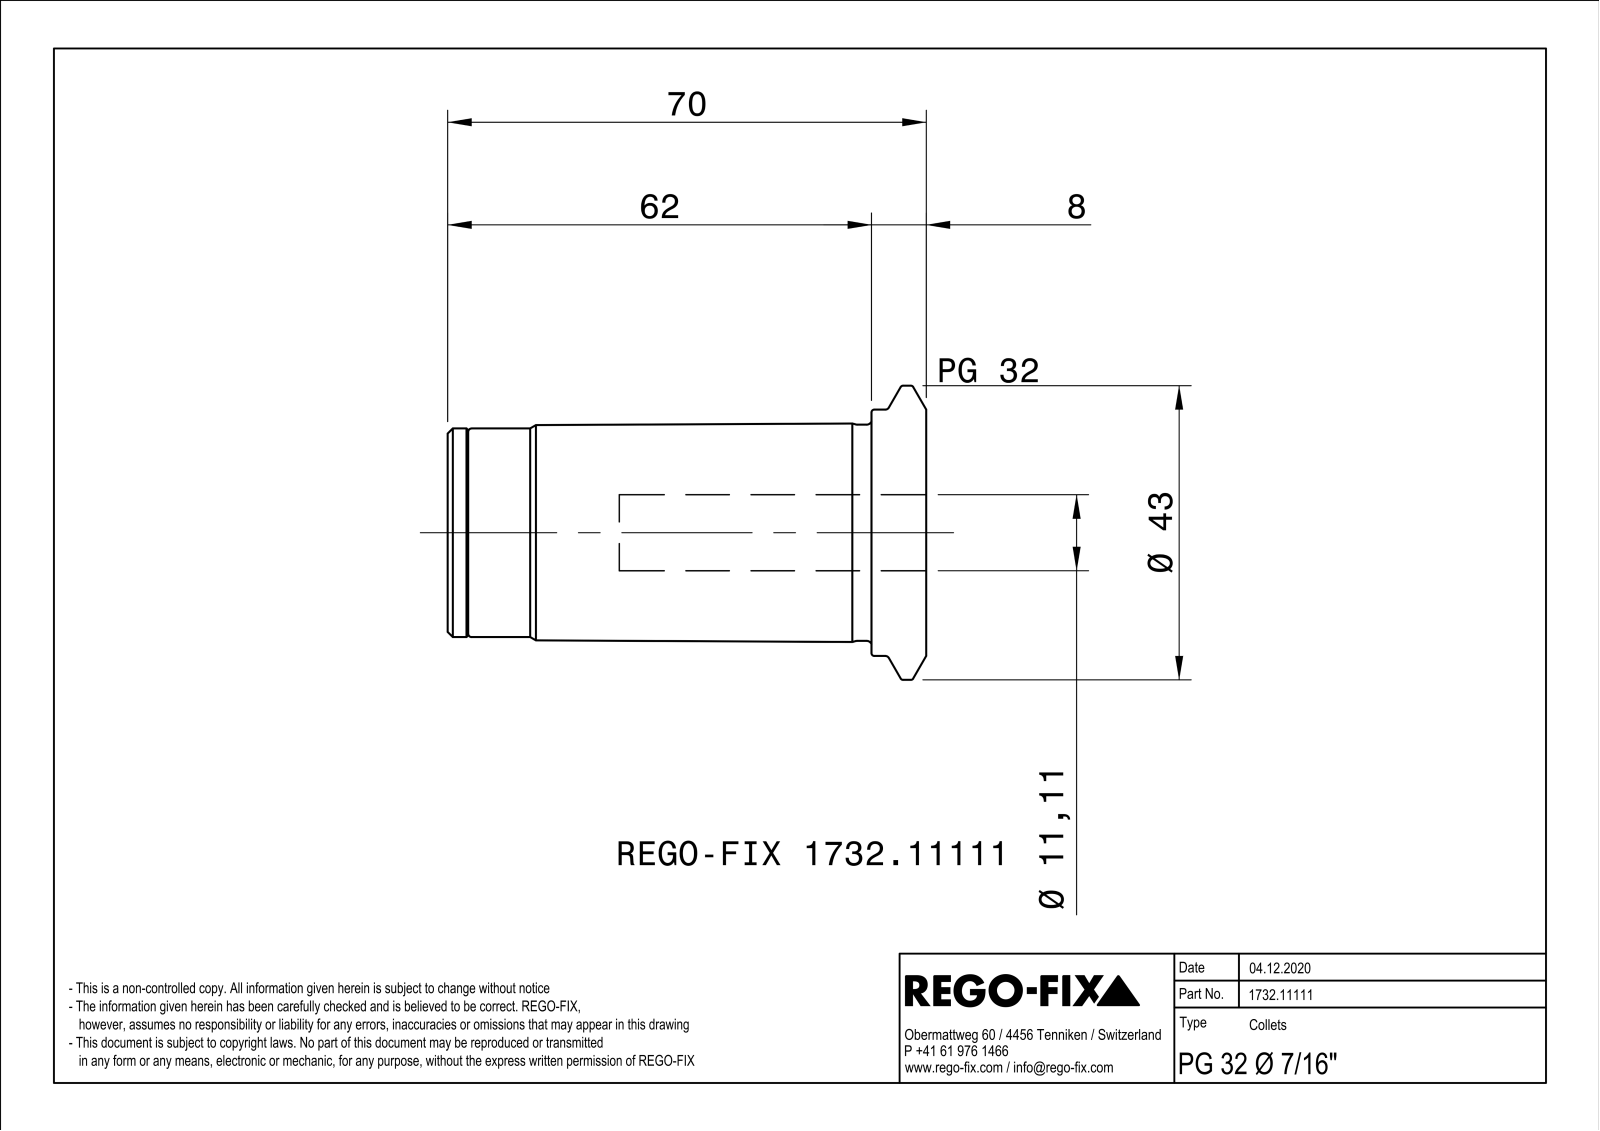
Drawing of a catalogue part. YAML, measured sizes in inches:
part_name: "NOCUT"
step_written_by: "SIEMENS PLM Software Solid Edge ST10 (AUTOMOTIVE_DESIGN)"
units: inches
bodies: {solids: 1, faces: 127, planar: 31, cylindrical: 41, other: 55}
overall_size: [2.756, 1.693, 1.693]
volume: 2.815
surface_area: 25.71
round_holes:
  - {diameter: 0.157, count: 3}
  - {diameter: 0.351, count: 1}
  - {diameter: 0.413, count: 1}
  - {diameter: 0.437, count: 1}
  - {diameter: 0.61, count: 1}
  - {diameter: 1.06, count: 1}
  - {diameter: 1.122, count: 1}
round_bosses_or_shafts:
  - {diameter: 1.693, count: 1}
  - {diameter: 1.417, count: 1}
  - {diameter: 1.244, count: 1}
  - {diameter: 1.201, count: 1}
  - {diameter: 1.043, count: 1}
  - {diameter: 0.827, count: 1}
partial_cylinders:
  - {radius: 0.079, count: 6}
  - {radius: 0.138, count: 3}
  - {radius: 0.157, count: 1}
  - {radius: 0.187, count: 1}
  - {radius: 0.344, count: 1}
face_to_face_distances: [0.039, 2.756, 2.283, 0.472, 2.323, 0.433, 0.315, 2.362, 0.079, 0.394]
hole_center_spacings: [0.305, 0.528, 0.529]
